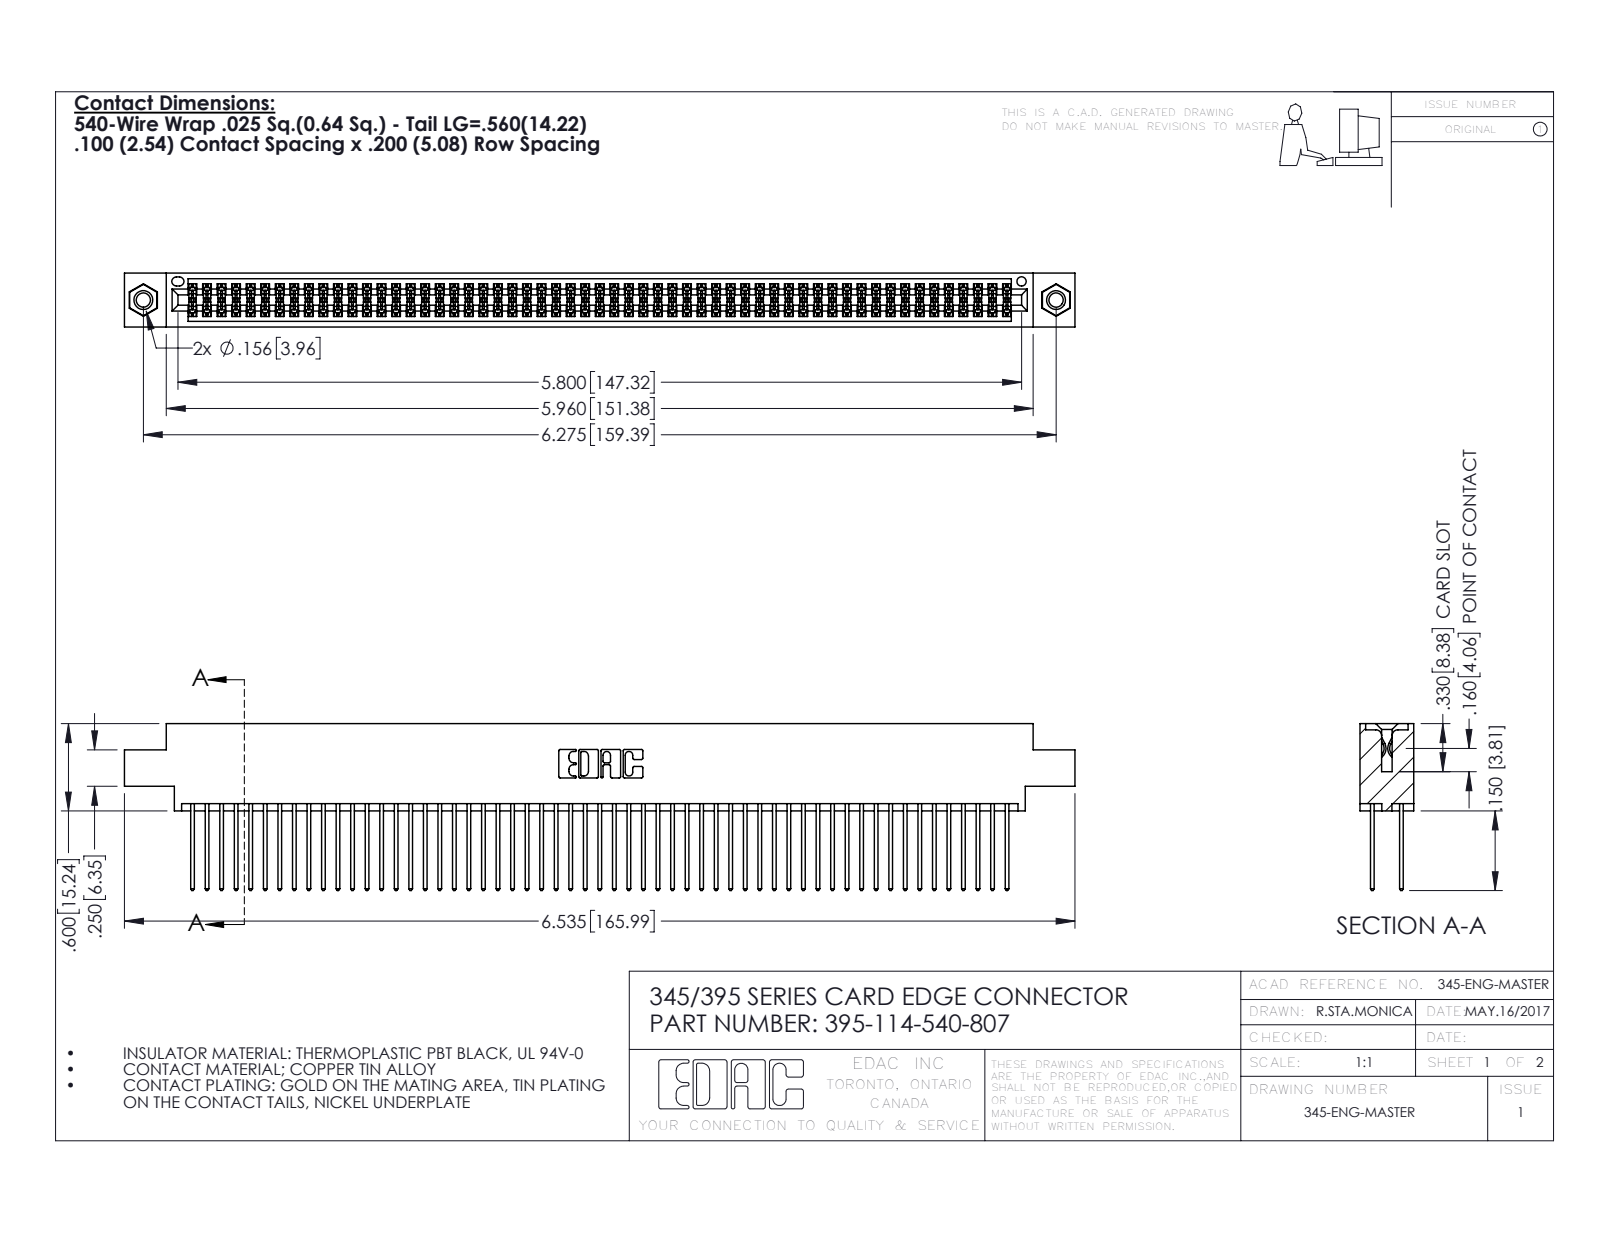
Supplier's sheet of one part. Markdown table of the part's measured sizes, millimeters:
| quantity | value |
| --- | --- |
| part name | 395-114-540-807; 345-250-001_345-250-005-103; 345 Part_0.170 Offset - 0.156 Dia-TI; 345-292-001_345-293-140 |
| STEP written by | SolidWorks 2016 (CONFIG_CONTROL_DESIGN) |
| units | millimeters |
| bodies | 117 solids, 5890 faces (3878 planar, 1996 cylindrical, 16 other) |
| overall size | 166 × 29.1 × 9.4 |
| volume | 16 570 mm³ |
| surface area | 26 960 mm² |
| round holes (diameter × count) | 2.5 × 2, 3.2 × 2, 4 × 2, 1.6 × 1 |
| round bosses / shafts (diameter × count) | 3.9 × 2 |
| partial cylindrical surfaces (radius × count) | 0.2 × 171, 0.3 × 114, 0.3 × 22, 0.2 × 6, 0.8 × 6, 0.7 × 3, 0.4 × 2, 0.5 × 2 |
| main face-to-face distances | 1.8, 7.6, 5.1, 2.5, 6.9, 0.6, 9.4, 5.7, 4.4, 3.8 |
| hole center spacings | 6.9, 153.4, 159.4 |
